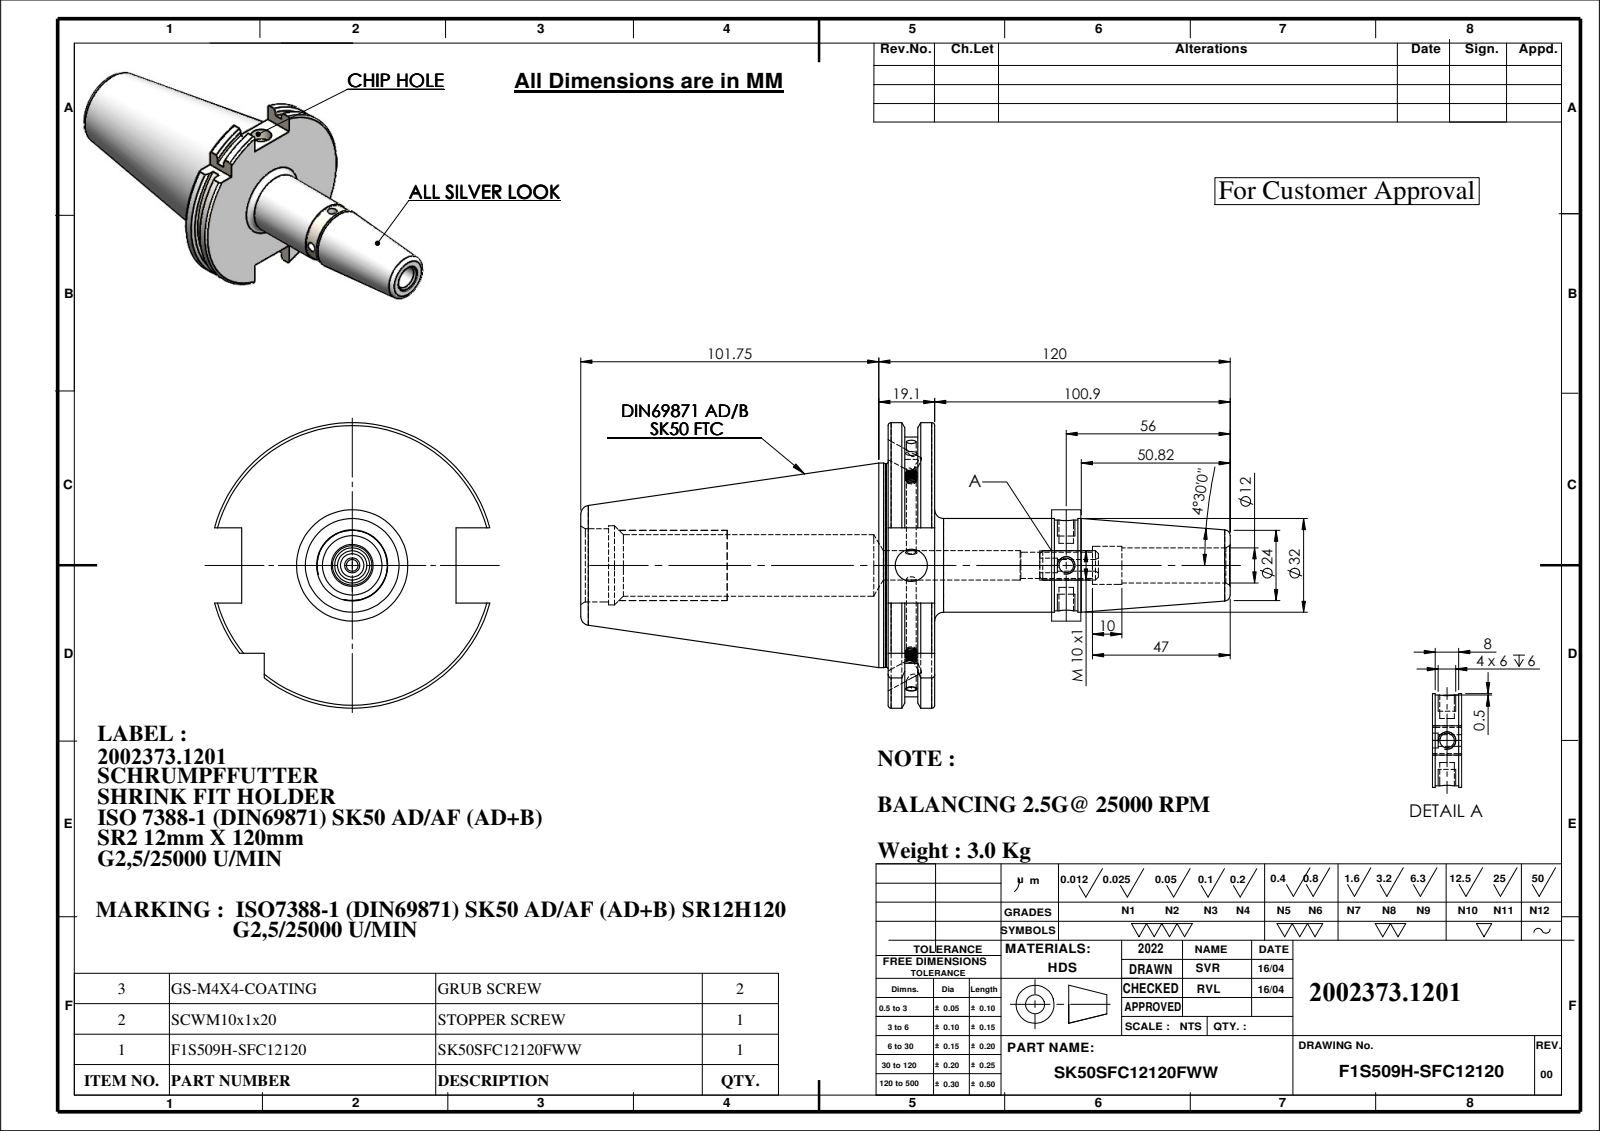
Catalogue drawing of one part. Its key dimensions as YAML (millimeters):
part_name: "91506-SR212120"
step_written_by: "SolidWorks 2018 (AUTOMOTIVE_DESIGN)"
units: millimeters
bodies: {solids: 1, faces: 122, planar: 29, cylindrical: 53, other: 40}
overall_size: [221.75, 97.5, 94.05]
volume: 396408
surface_area: 56006
round_holes:
  - {diameter: 5, count: 2}
  - {diameter: 6, count: 2}
  - {diameter: 3.3, count: 1}
  - {diameter: 9, count: 1}
  - {diameter: 11, count: 1}
  - {diameter: 11.99, count: 1}
  - {diameter: 13, count: 1}
  - {diameter: 21, count: 1}
  - {diameter: 25, count: 1}
  - {diameter: 27, count: 1}
round_bosses_or_shafts:
  - {diameter: 69.85, count: 1}
  - {diameter: 69.45, count: 1}
  - {diameter: 32, count: 1}
partial_cylinders:
  - {radius: 44.9, count: 1}
  - {radius: 48.75, count: 1}
face_to_face_distances: [15.9, 5.66, 10.24, 10.14, 4.48, 5.76, 104.95, 110.61, 115.09, 120.85]
hole_center_spacings: [48.9]
